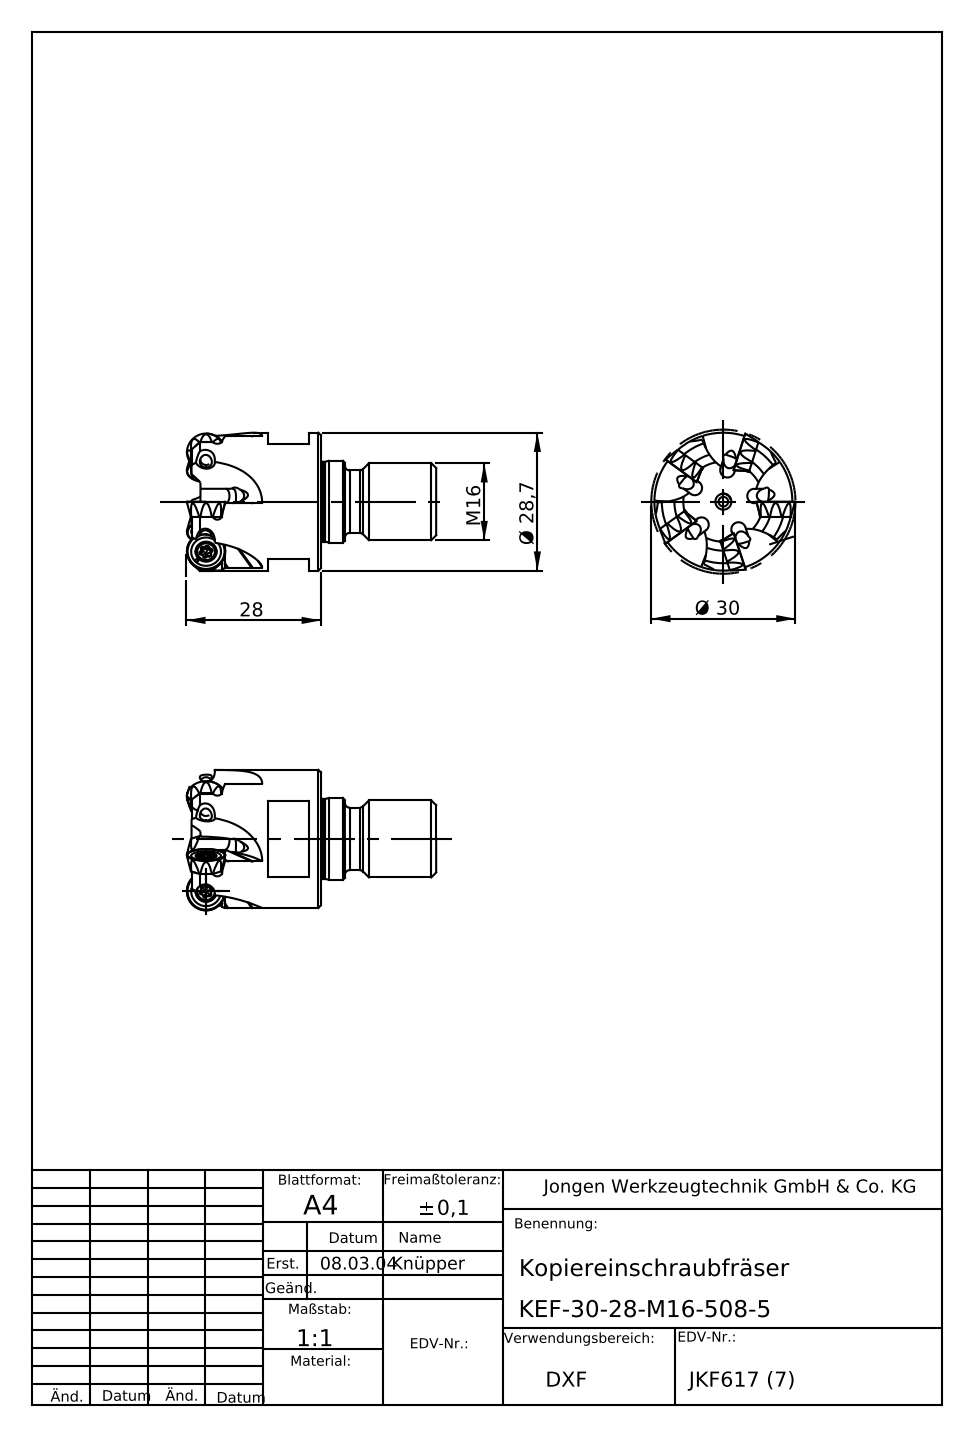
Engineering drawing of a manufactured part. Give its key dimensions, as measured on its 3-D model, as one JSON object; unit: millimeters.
{"part_name": "KEF_30_28_M16_508_5", "step_written_by": "SolidWorks 2016 (AUTOMOTIVE_DESIGN)", "units": "millimeters", "bodies": {"solids": 1, "faces": 210, "planar": 90, "cylindrical": 68, "other": 52}, "overall_size": [51.99, 29.97, 29.97], "volume_mm3": 19703, "surface_area_mm2": 6785, "round_holes": [[3, 5], [2, 1], [4, 1]], "round_bosses_or_shafts": [[28.7, 1], [17, 1], [16.6, 1], [16, 1], [13, 1]], "partial_cylinders_radius": [[1.5, 10], [1, 5]], "face_to_face_distances": [24, 49.05, 25.05, 26.5, 2.5, 22.55, 35, 11, 8.5, 14.05]}
